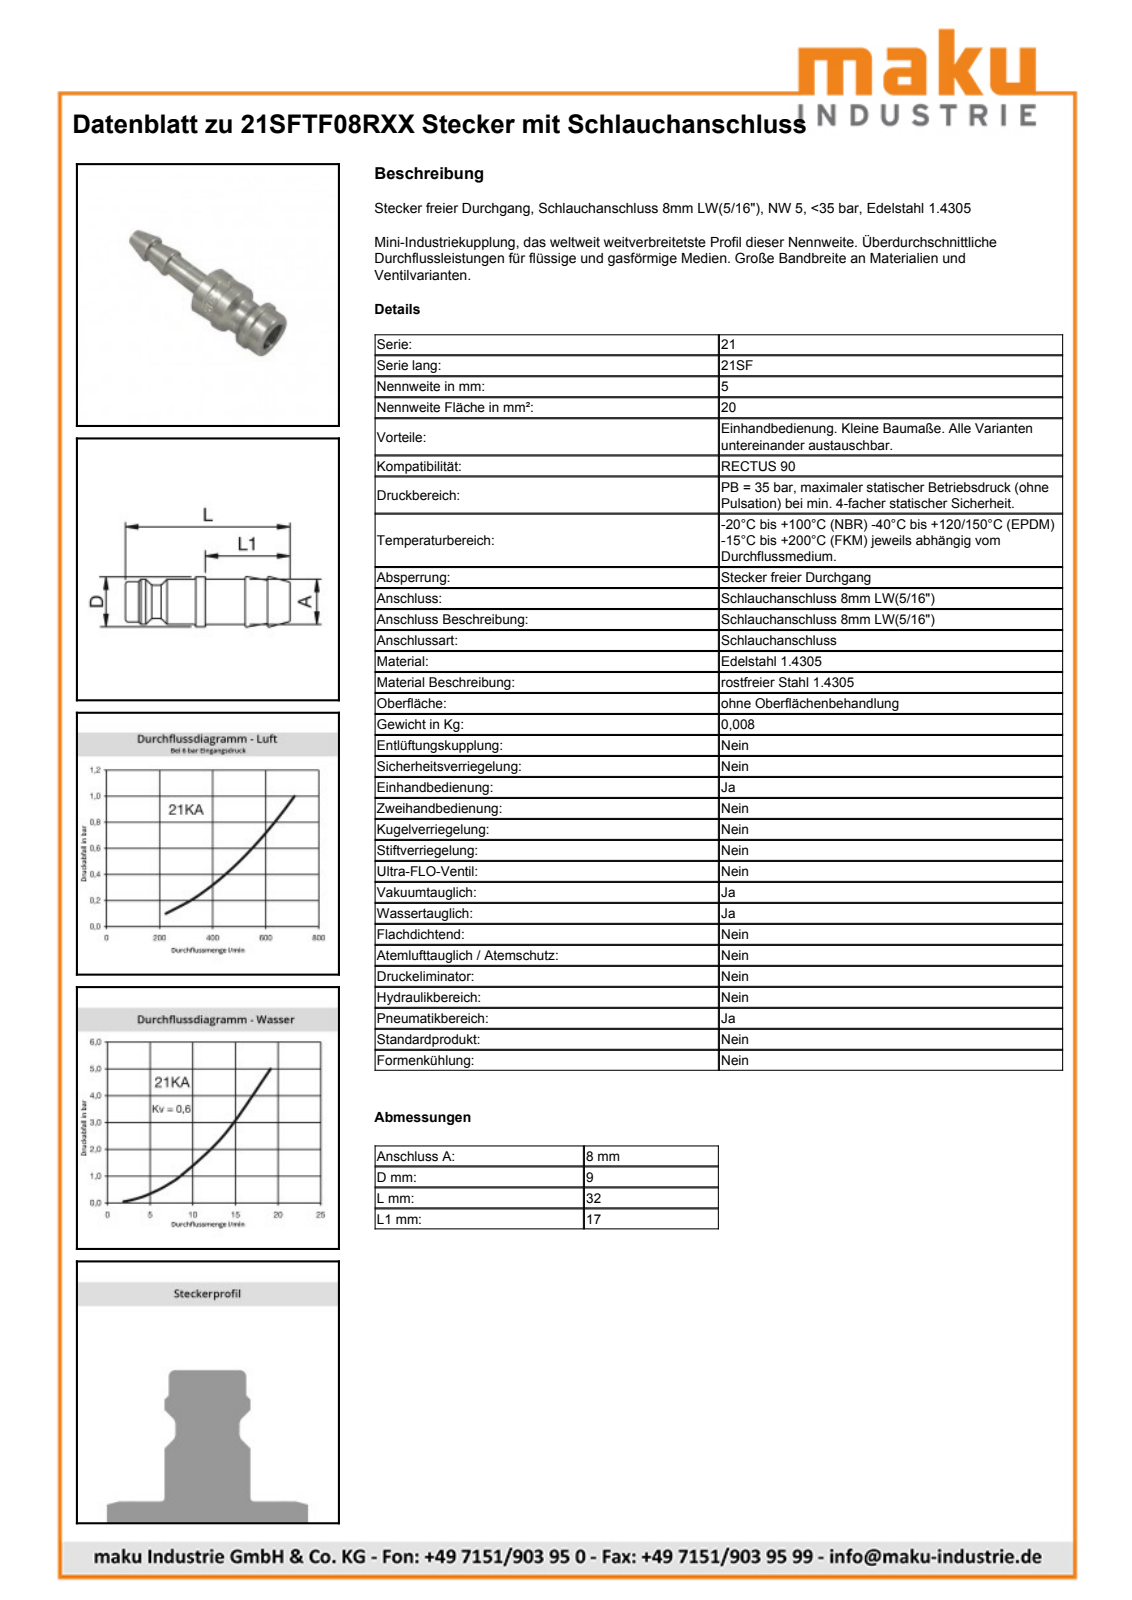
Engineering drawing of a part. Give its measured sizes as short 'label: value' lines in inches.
name: D107136
written by: Autodesk Inventor 2013 (AUTOMOTIVE_DESIGN)
unit: in
bodies: 2 solids, 29 faces (7 planar, 6 cylindrical, 16 other)
size: 1.26 × 0.356 × 0.356
volume: 0.065 in³; area: 2.303 in²
holes: 1× ⌀0.195
bosses: 1× ⌀0.354, 1× ⌀0.319, 1× ⌀0.315, 1× ⌀0.262
face distances: 0.177, 1.083, 0.906, 1.26, 0.354, 0.591, 0.315, 0.492, 0.669
